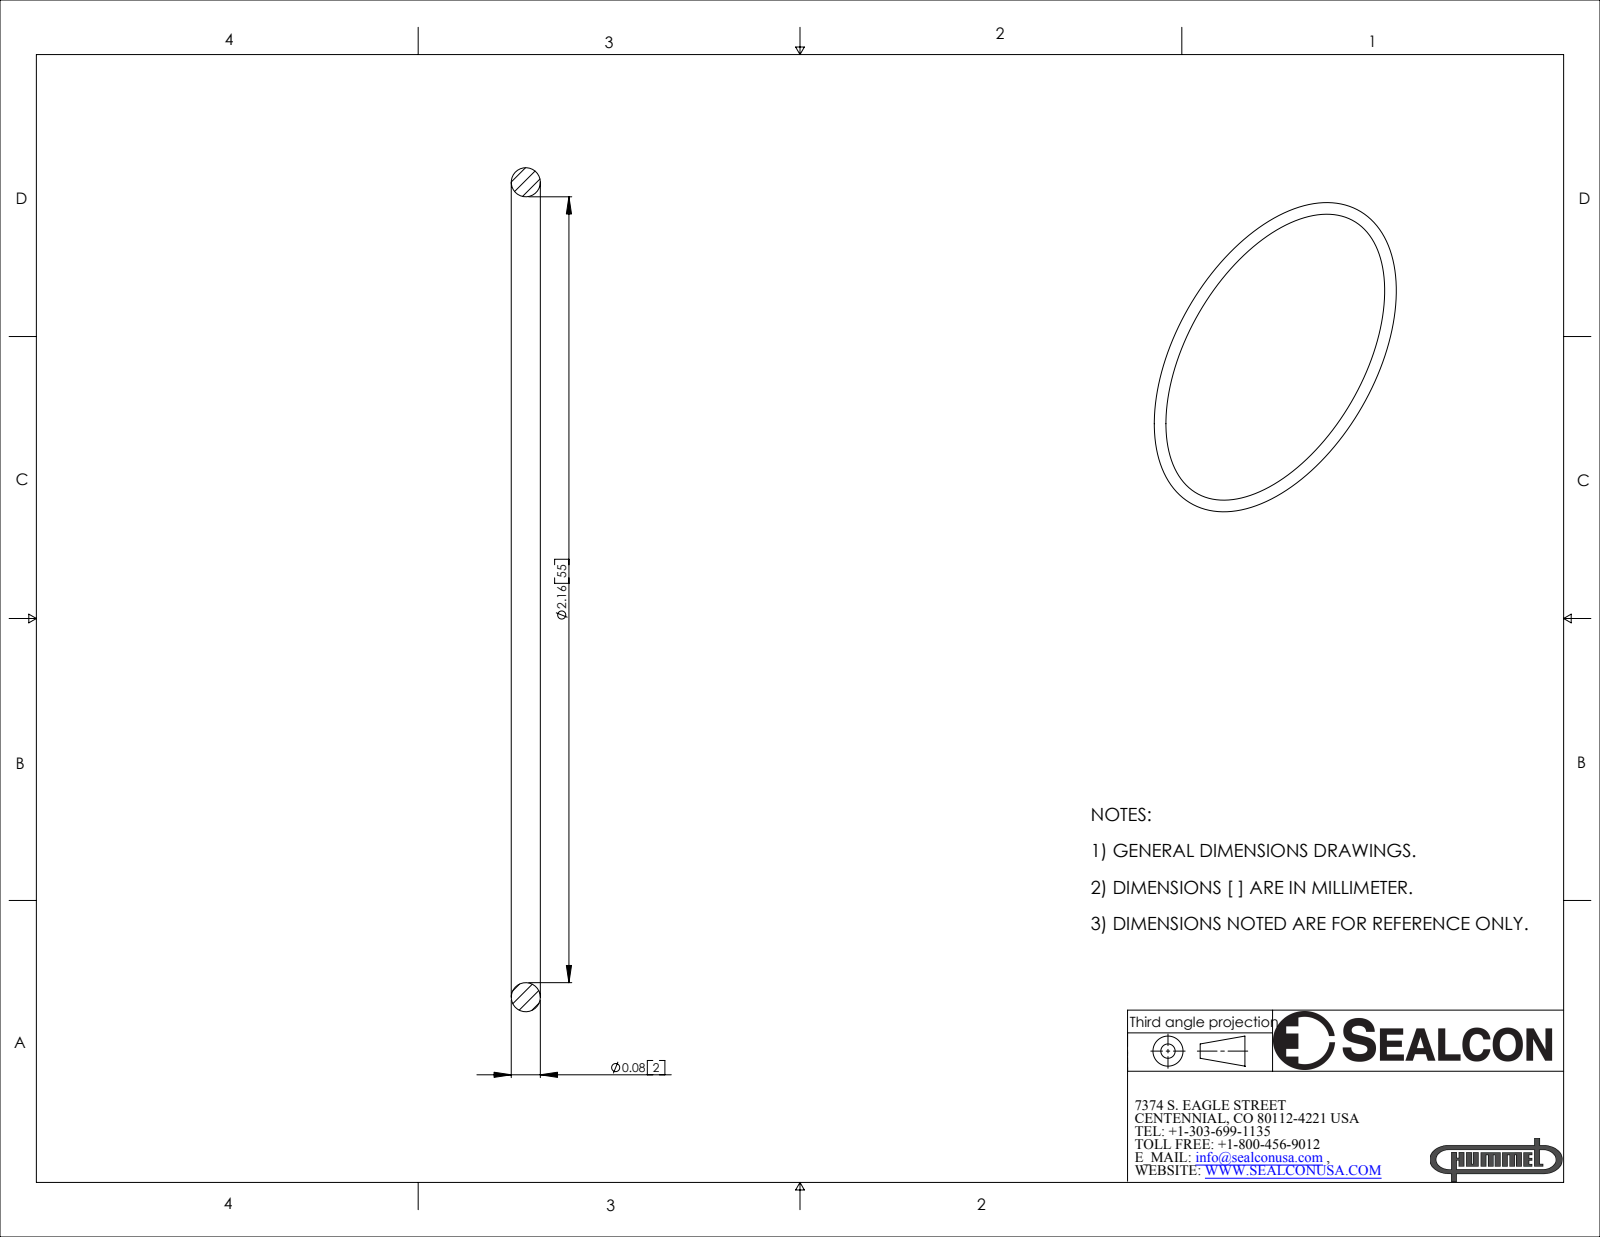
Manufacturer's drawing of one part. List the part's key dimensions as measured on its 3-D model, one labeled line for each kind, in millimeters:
Part name (STEP PRODUCT): OM-63-BN
STEP written by: SolidWorks 2007 (CONFIG_CONTROL_DESIGN)
Units: millimetres
Bodies: 1 solid, 4 faces (0 planar, 0 cylindrical, 4 other)
Overall size (bounding box): 58.9 × 58.9 × 2
Volume: 570 mm³ · Surface area: 1 141 mm²
